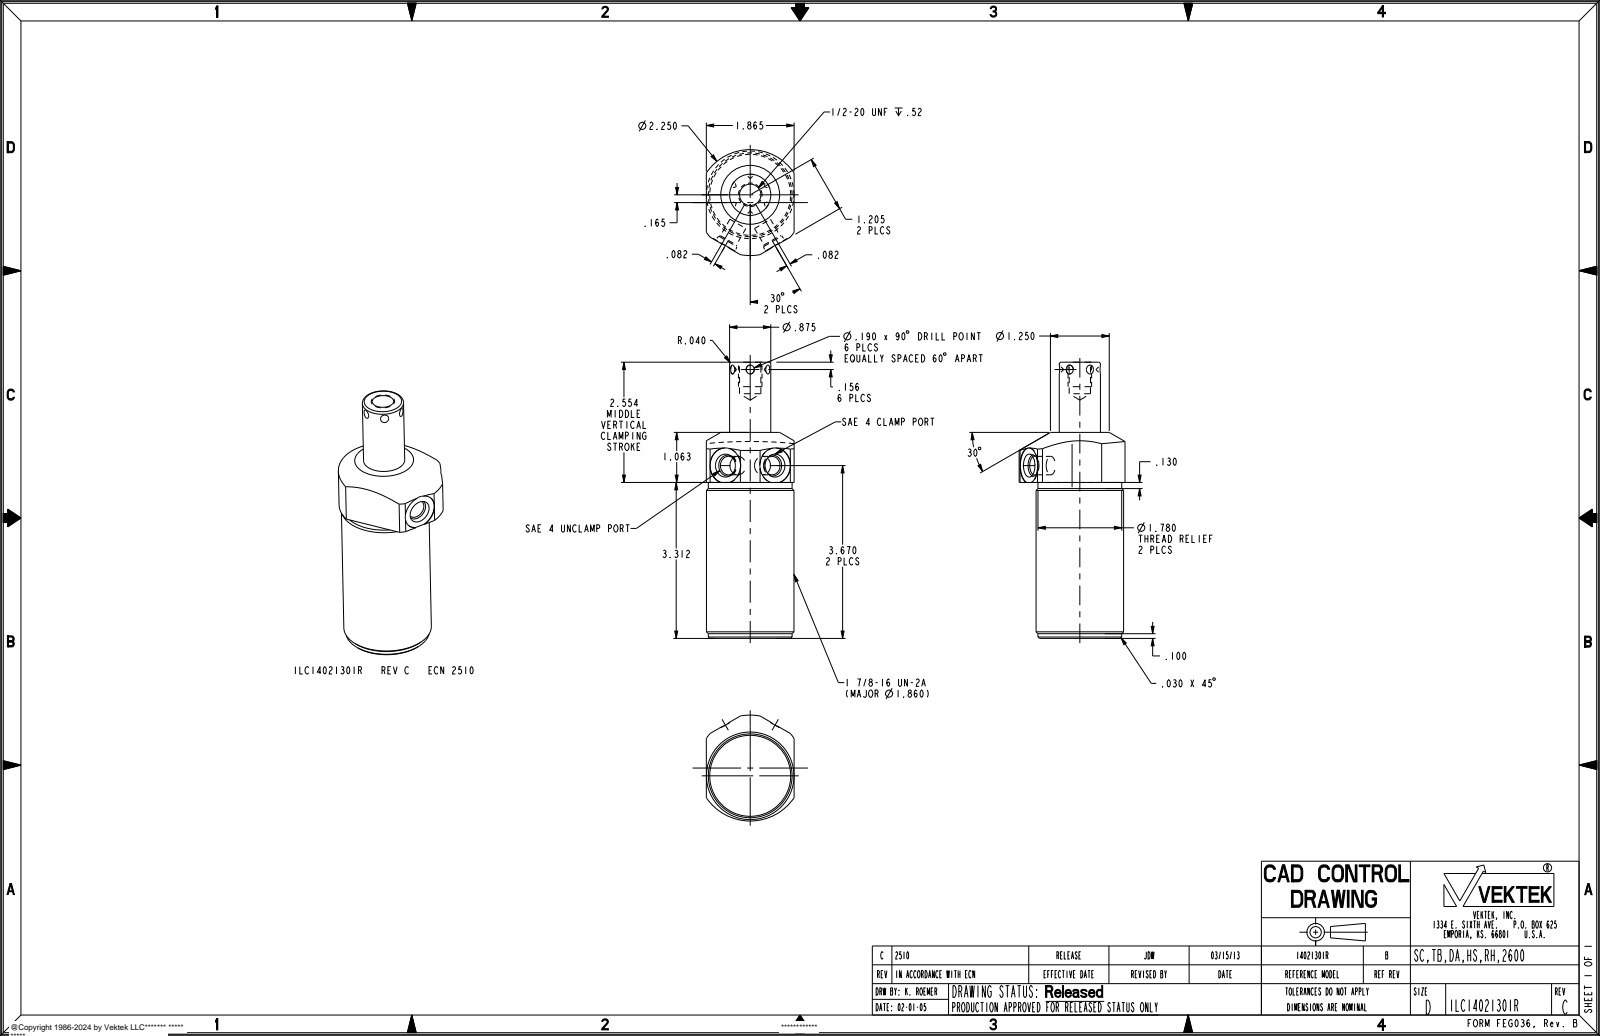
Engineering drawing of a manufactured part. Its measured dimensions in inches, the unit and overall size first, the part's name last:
Units: inches
Overall size (bounding box): 5.866 × 2.25 × 1.865
Round holes (diameter × count): ⌀0.392 ×2, ⌀0.75 ×2, ⌀0.453 ×1
Round bosses / shafts (diameter × count): ⌀1.86 ×1, ⌀1.78 ×1, ⌀0.875 ×1, ⌀0.5 ×1
Partial cylindrical surfaces — rounded edges, fillets, slot ends (radius × count): R1.125 ×1
Main face-to-face distances: 3.312, 1.865, 4.375, 1.063, 5.866, 2.554, 1.491, 0.53, 0.54, 5.346
Volume: 13.02 in³ · Surface area: 39.68 in²
Bodies: 1 solid, 75 faces (19 planar, 24 cylindrical, 32 other)
Part name (STEP PRODUCT): ILC14021301R
STEP written by: PRO/ENGINEER BY PARAMETRIC TECHNOLOGY CORPORATION, 2007460 (AUTOMOTIVE_DESIGN_CC2)
